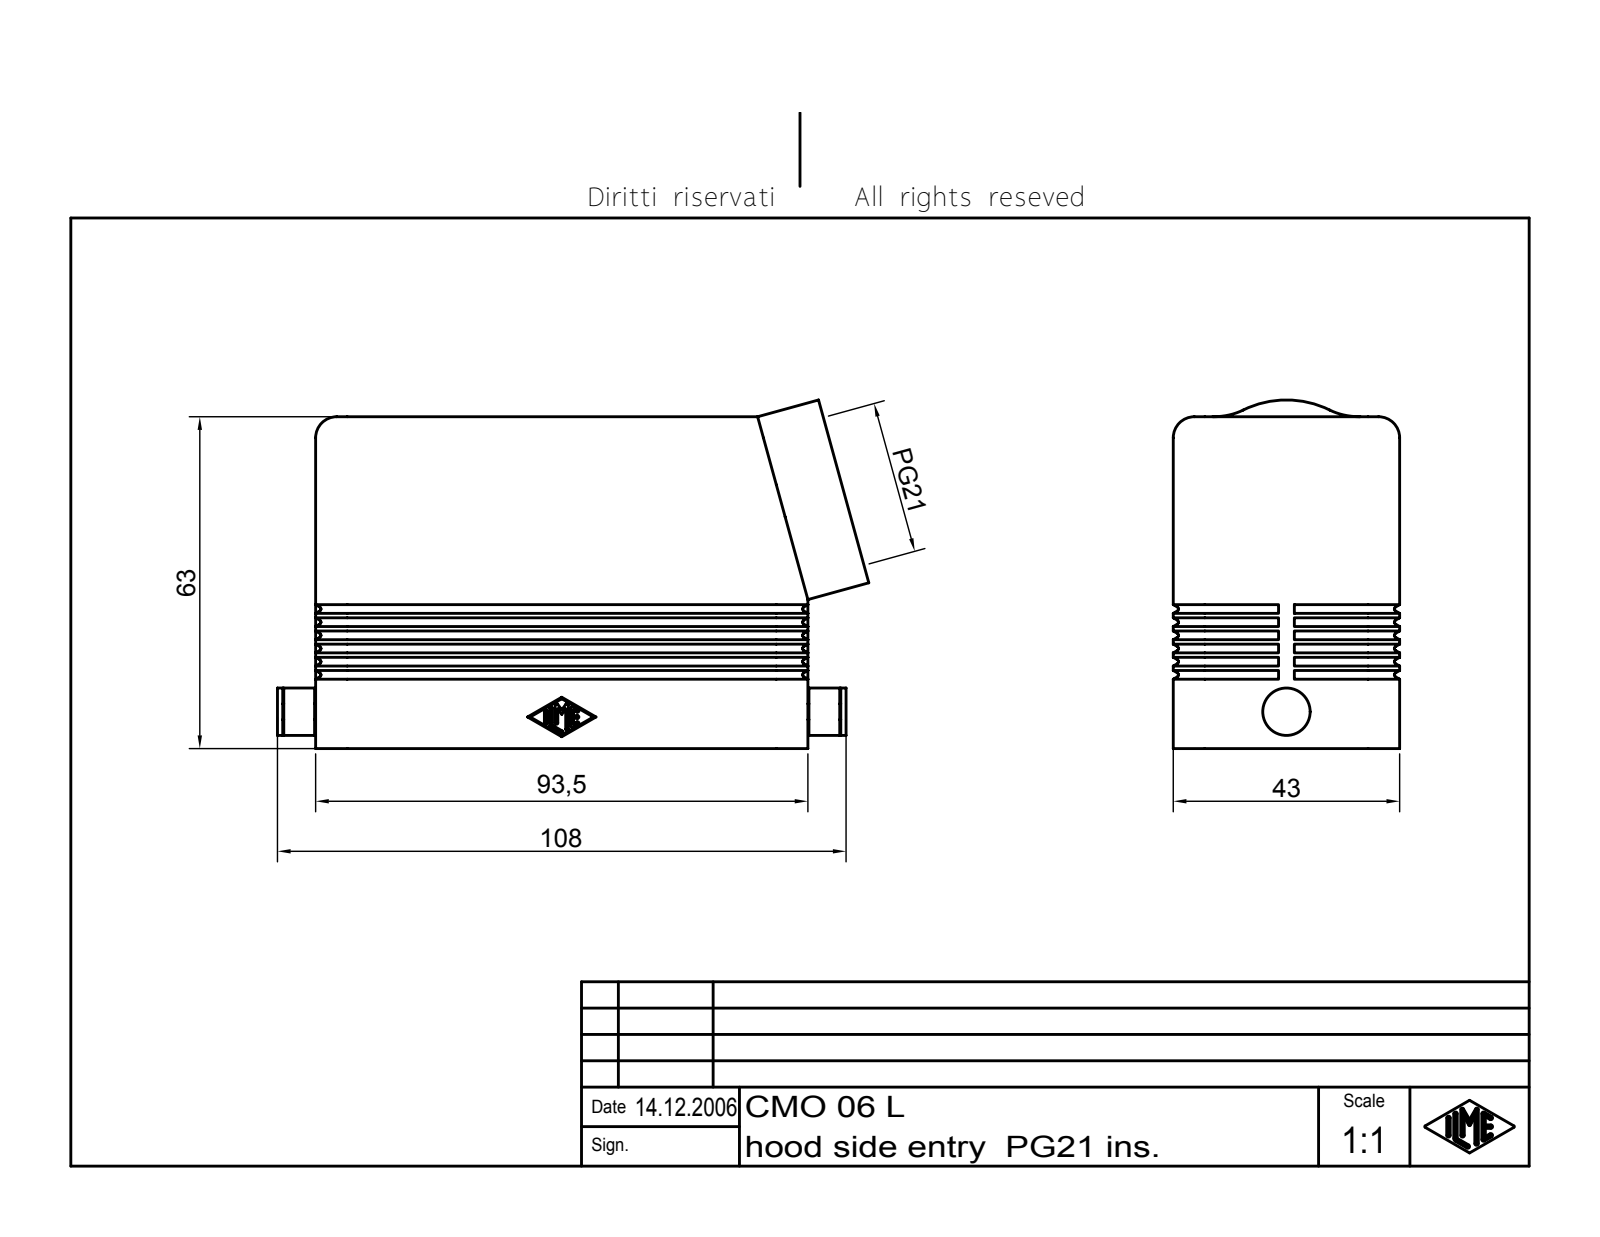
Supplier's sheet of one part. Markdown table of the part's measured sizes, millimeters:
| quantity | value |
| --- | --- |
| part name | CMO 06 L |
| STEP written by | Autodesk Inventor 7 (AUTOMOTIVE_DESIGN) |
| units | millimeters |
| bodies | 1 solid, 633 faces (147 planar, 262 cylindrical, 224 other) |
| overall size | 112.32 × 66.18 × 43 |
| volume | 73 206 mm³ |
| surface area | 42 396 mm² |
| round holes (diameter × count) | 21.5 × 1, 26.78 × 1 |
| round bosses / shafts (diameter × count) | 9 × 1, 3 × 1 |
| partial cylindrical surfaces (radius × count) | 0.4 × 48, 0.25 × 14, 1.5 × 4, 3 × 4, 6 × 4, 4 × 3, 5 × 2 |
| main face-to-face distances | 3, 40, 37, 43, 8.25, 79.25, 82.25, 11.25, 90.5, 11.5 |
